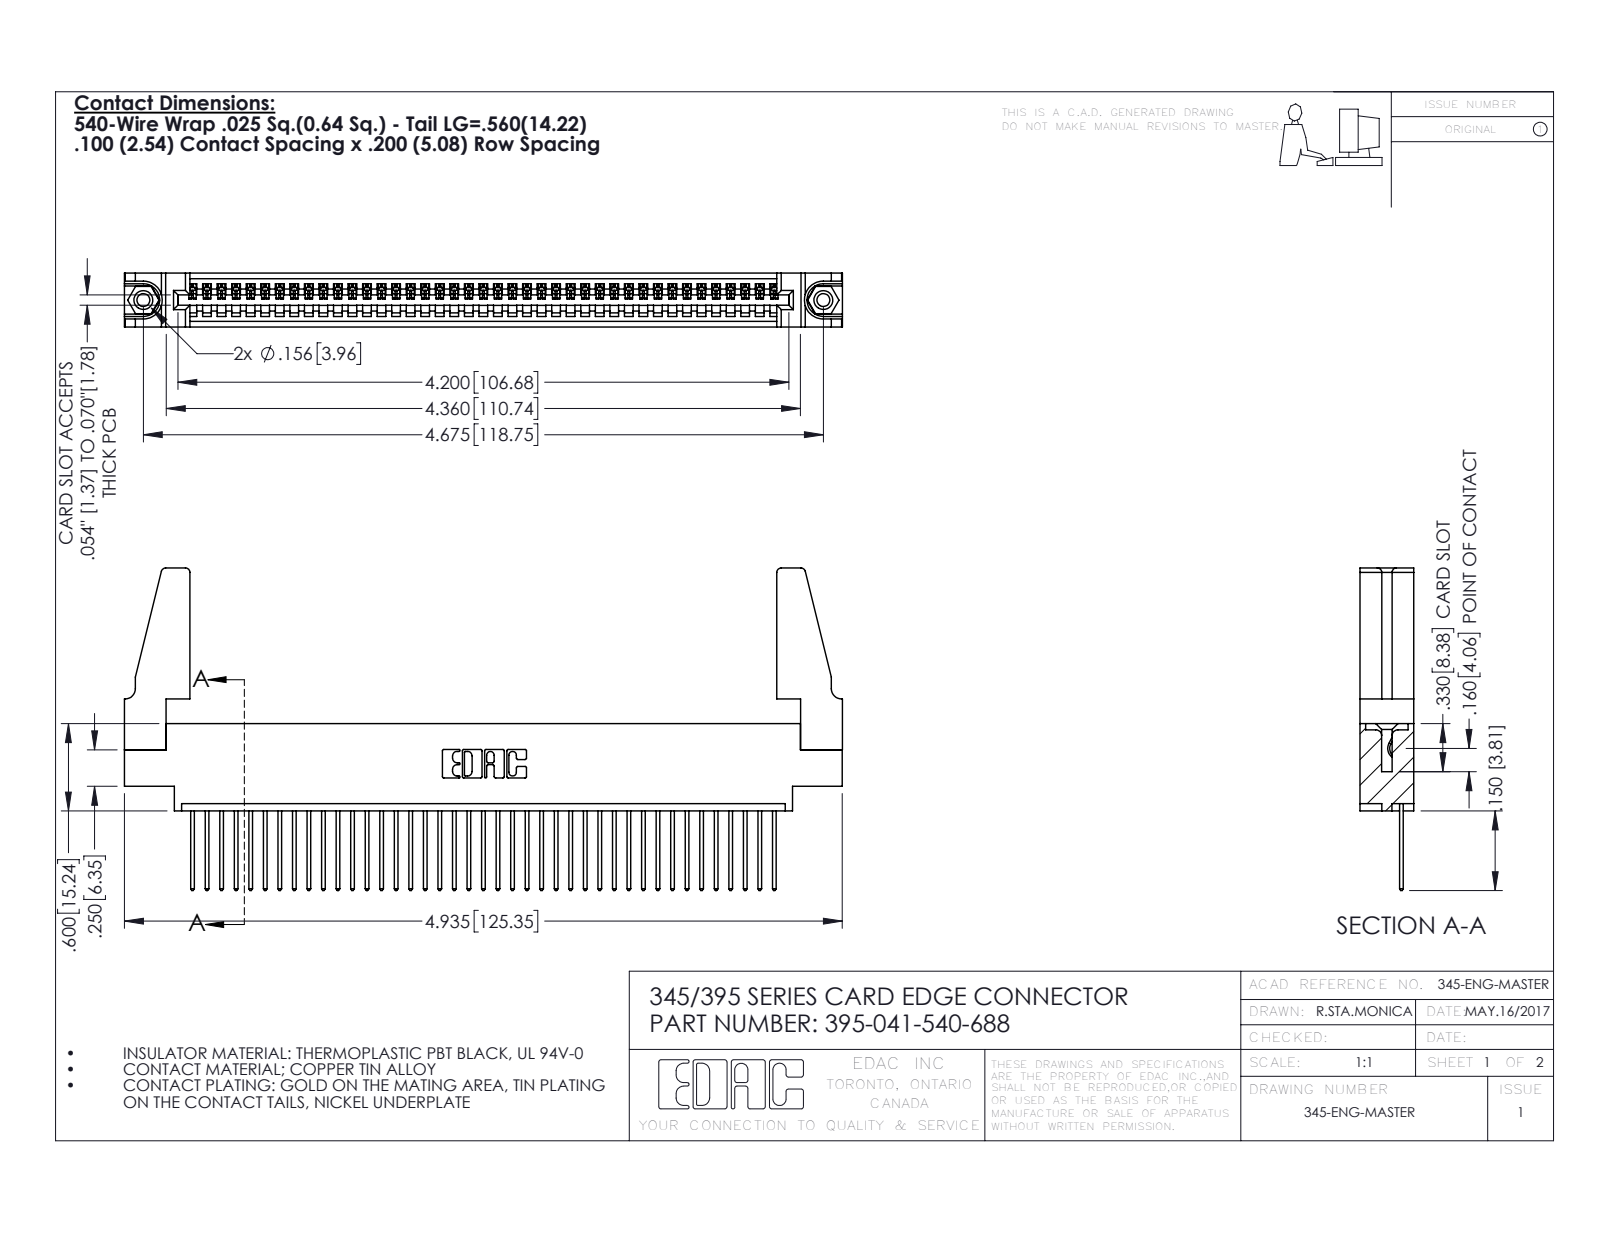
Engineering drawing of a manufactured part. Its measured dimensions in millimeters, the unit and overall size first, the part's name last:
Units: millimetres
Overall size (bounding box): 125.4 × 56.3 × 9.4
Round holes (diameter × count): ⌀2.3 ×2, ⌀3.2 ×2, ⌀4 ×2, ⌀1.6 ×1
Round bosses / shafts (diameter × count): ⌀3.9 ×2
Partial cylindrical surfaces — rounded edges, fillets, slot ends (radius × count): R0.2 ×82, R0.3 ×82, R0.3 ×22, R0.8 ×8, R0.2 ×6, R0.8 ×6, R0.7 ×3, R0.8 ×2
Main face-to-face distances: 1.8, 7.6, 9.4, 2.5, 6.9, 0.6, 5.1, 5.7, 4.4, 3.8
Hole centre spacings: 6.9, 112.8, 118.7
Volume: 15 100 mm³ · Surface area: 19 380 mm²
Bodies: 46 solids, 2632 faces (1796 planar, 820 cylindrical, 16 other)
Part name (STEP PRODUCT): 345-250-001_345-250-001-102; 345-292-001_345-293-140; 395-041-540-688; 345 Part_0.170 Offset - 0.156 Dia-TH (+1 more)
STEP written by: SolidWorks 2016 (CONFIG_CONTROL_DESIGN)
